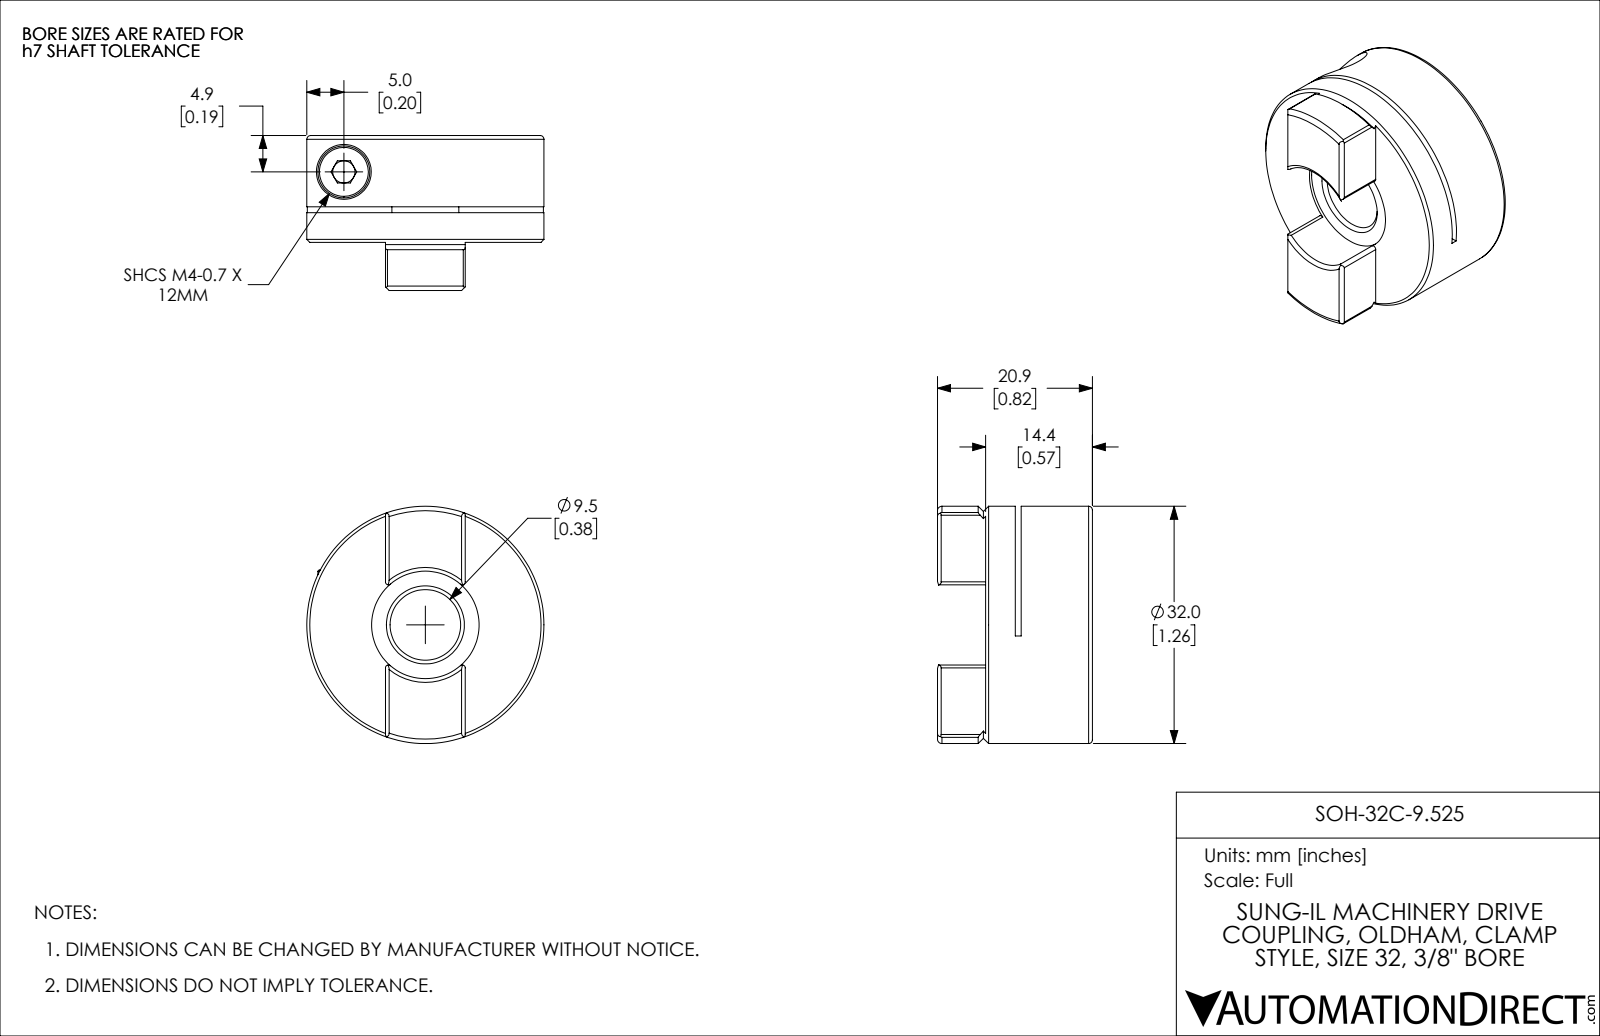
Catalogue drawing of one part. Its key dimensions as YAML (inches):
part_name: "SOH-32C-9.525"
step_written_by: "SolidWorks 2021 (CONFIG_CONTROL_DESIGN)"
units: inches
bodies: {solids: 2, faces: 99, planar: 39, cylindrical: 33, other: 27}
overall_size: [1.26, 1.26, 0.823]
volume: 0.676
surface_area: 8.445
round_holes:
  - {diameter: 0.118, count: 1}
  - {diameter: 0.13, count: 1}
  - {diameter: 0.173, count: 1}
  - {diameter: 0.291, count: 1}
  - {diameter: 0.375, count: 1}
  - {diameter: 0.571, count: 1}
round_bosses_or_shafts:
  - {diameter: 1.26, count: 1}
  - {diameter: 0.276, count: 1}
  - {diameter: 0.157, count: 1}
partial_cylinders:
  - {radius: 0.016, count: 8}
  - {radius: 0.984, count: 1}
face_to_face_distances: [0.157, 0.567, 0.409, 0.378, 0.031, 0.189, 0.039, 0.823, 0.445, 0.413]
